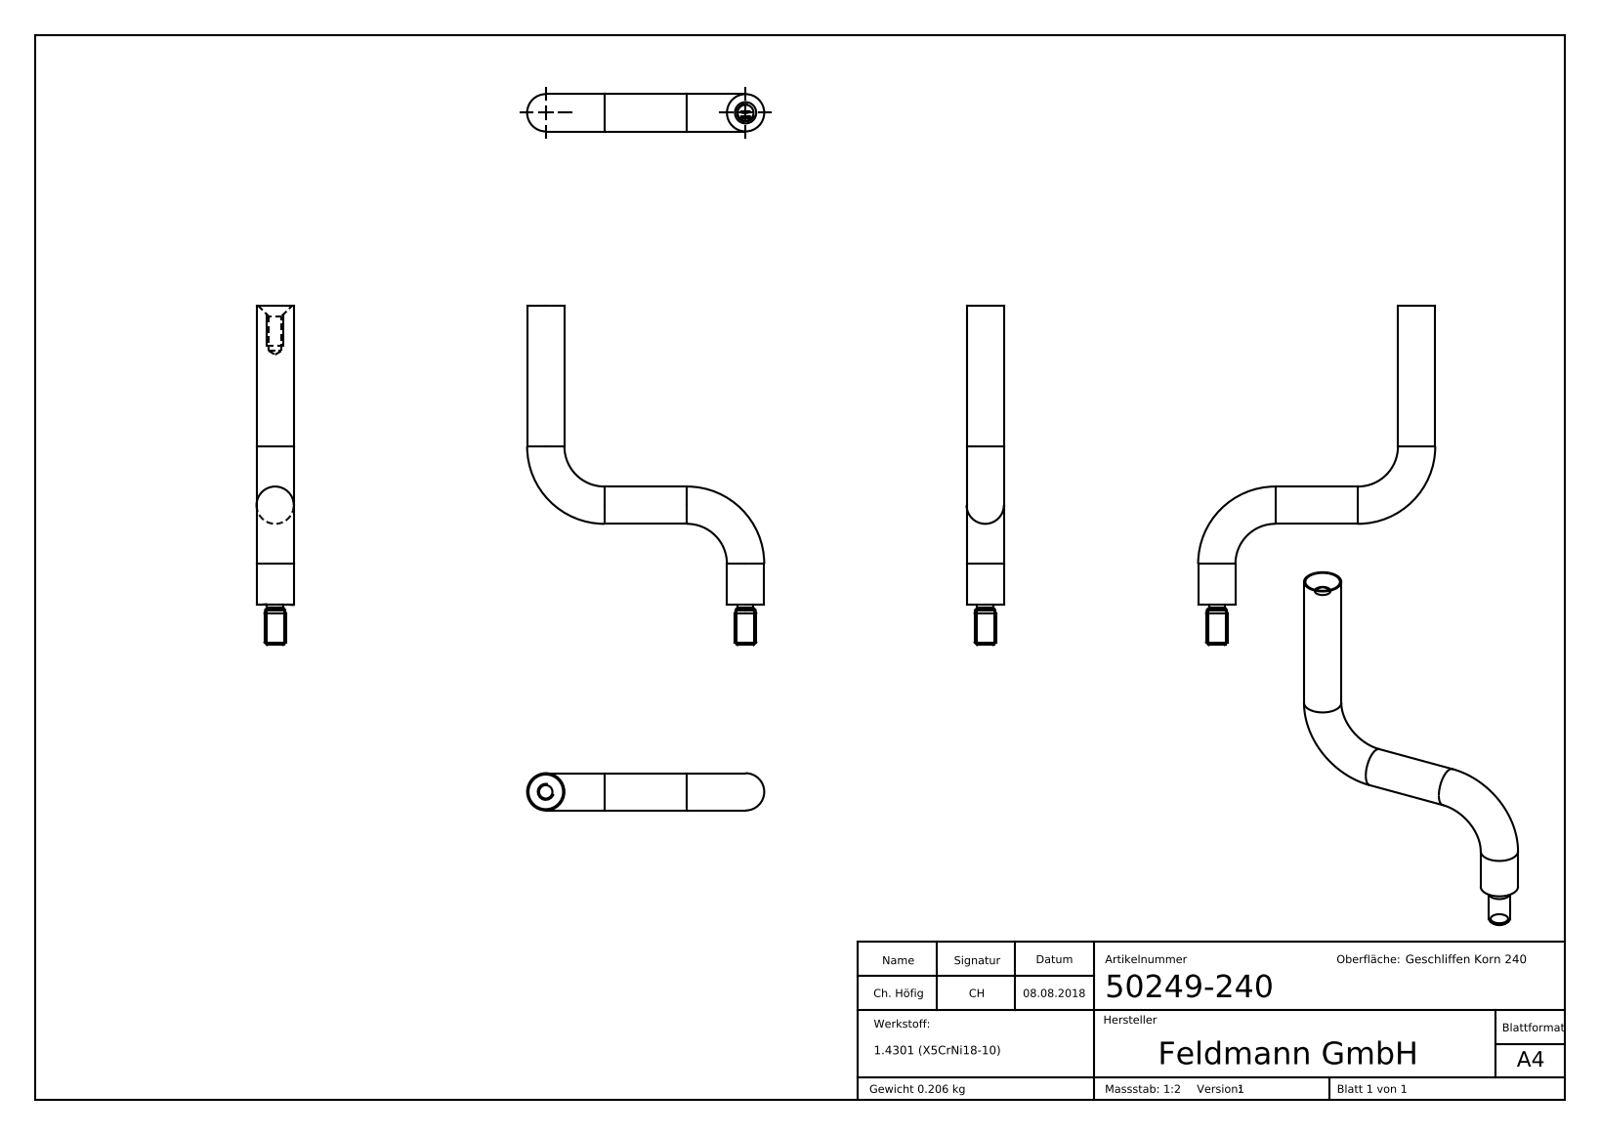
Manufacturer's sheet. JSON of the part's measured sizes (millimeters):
{"part_name": "50249-240", "step_written_by": "SolidWorks 2015 (CONFIG_CONTROL_DESIGN)", "units": "millimeters", "bodies": {"solids": 1, "faces": 265, "planar": 132, "cylindrical": 14, "other": 119}, "overall_size": [127.5, 89, 14], "volume_mm3": 26104, "surface_area_mm2": 8365, "round_holes": [[5, 1]], "round_bosses_or_shafts": [[14, 3], [8, 1], [6.46, 1], [6, 1]], "face_to_face_distances": [127.5, 127.4, 1.19, 1.46, 1.88, 1.2, 1.47, 2.12, 0.66, 1.94]}
